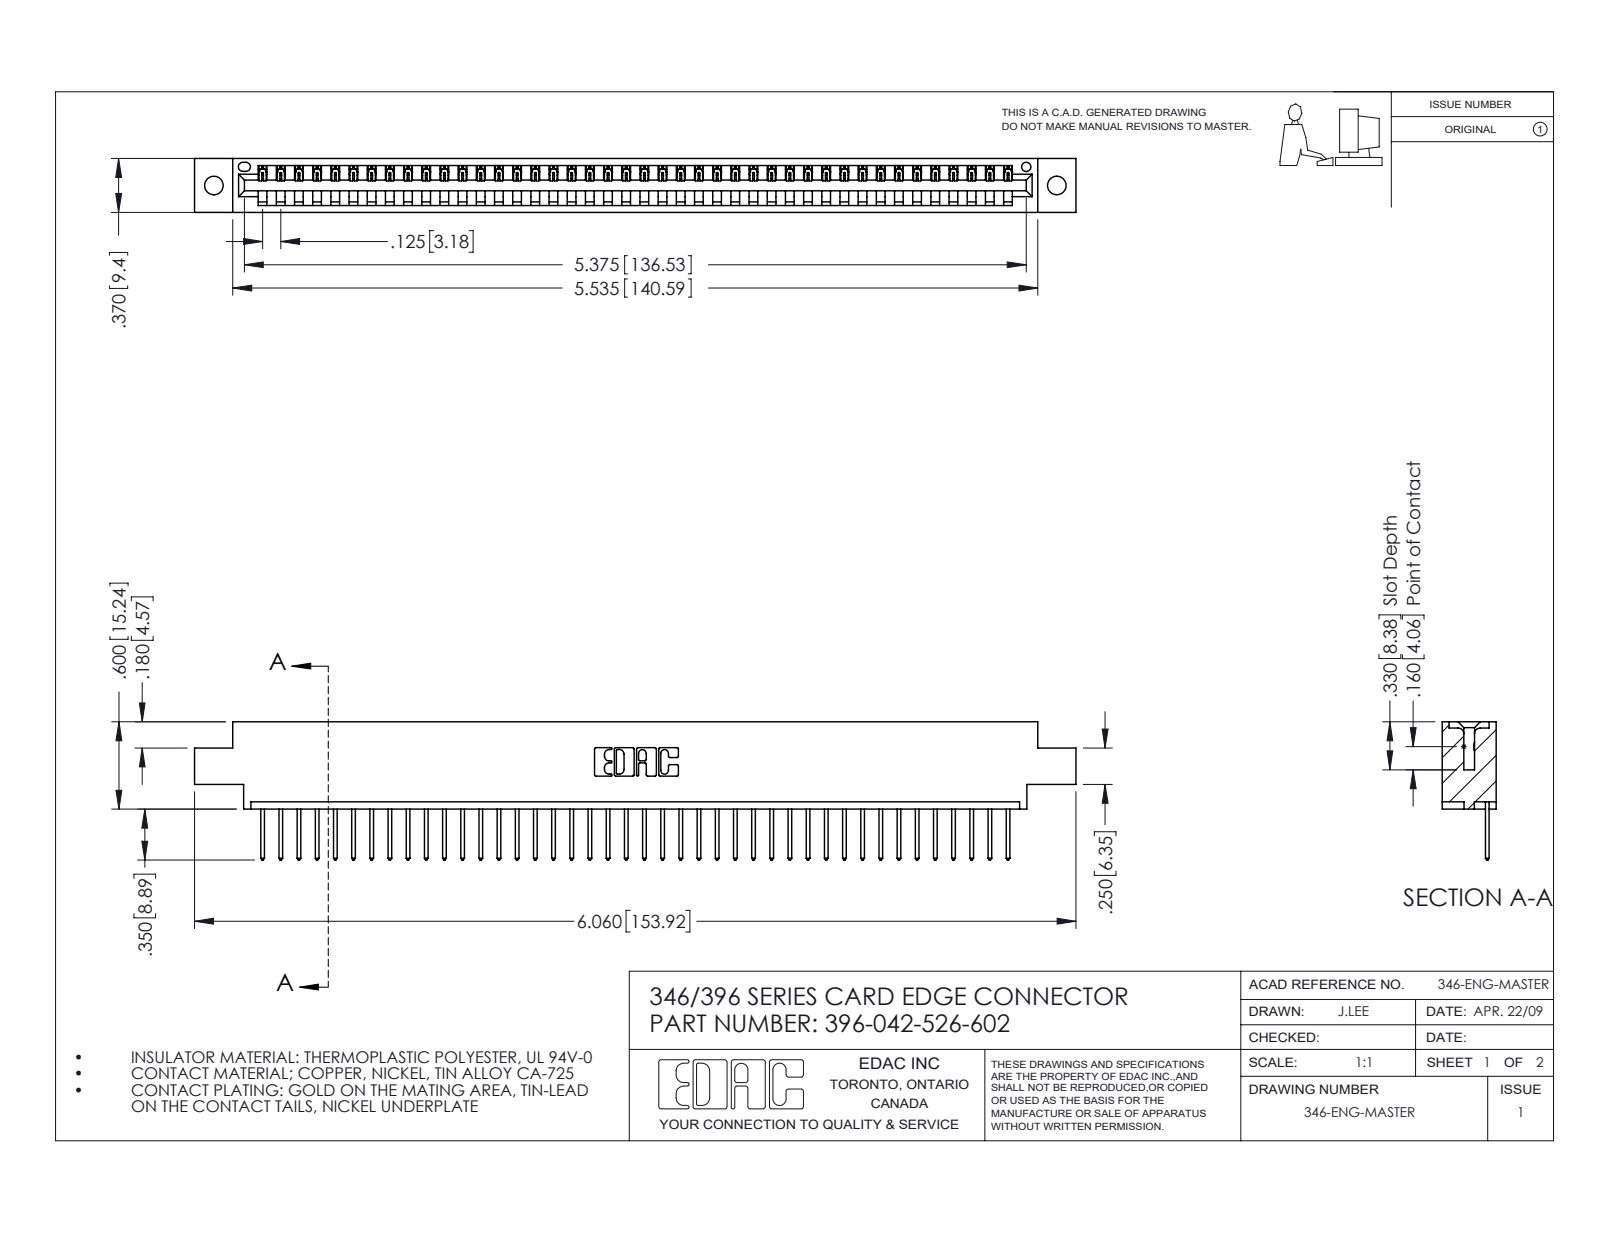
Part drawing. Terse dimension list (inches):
name: 345-292-001_345-293-126; 396-042-526-602; 346 Part_0.170 Offset - 0.128 Dia
written by: SolidWorks 2016 (CONFIG_CONTROL_DESIGN)
unit: in
bodies: 43 solids, 2562 faces (1760 planar, 802 cylindrical, 0 other)
size: 6.06 × 0.95 × 0.37
volume: 0.885 in³; area: 27.87 in²
holes: 2× ⌀0.128, 1× ⌀0.064
rounds: 84× R0.006, 84× R0.01, 22× R0.01, 6× R0.007, 6× R0.031, 3× R0.026, 2× R0.031, 2× R0.04
face distances: 0.048, 0.322, 0.37, 0.25, 0.072, 0.298, 0.025, 0.148, 0.222, 0.1
hole spacings: 0.246, 5.586, 5.795
